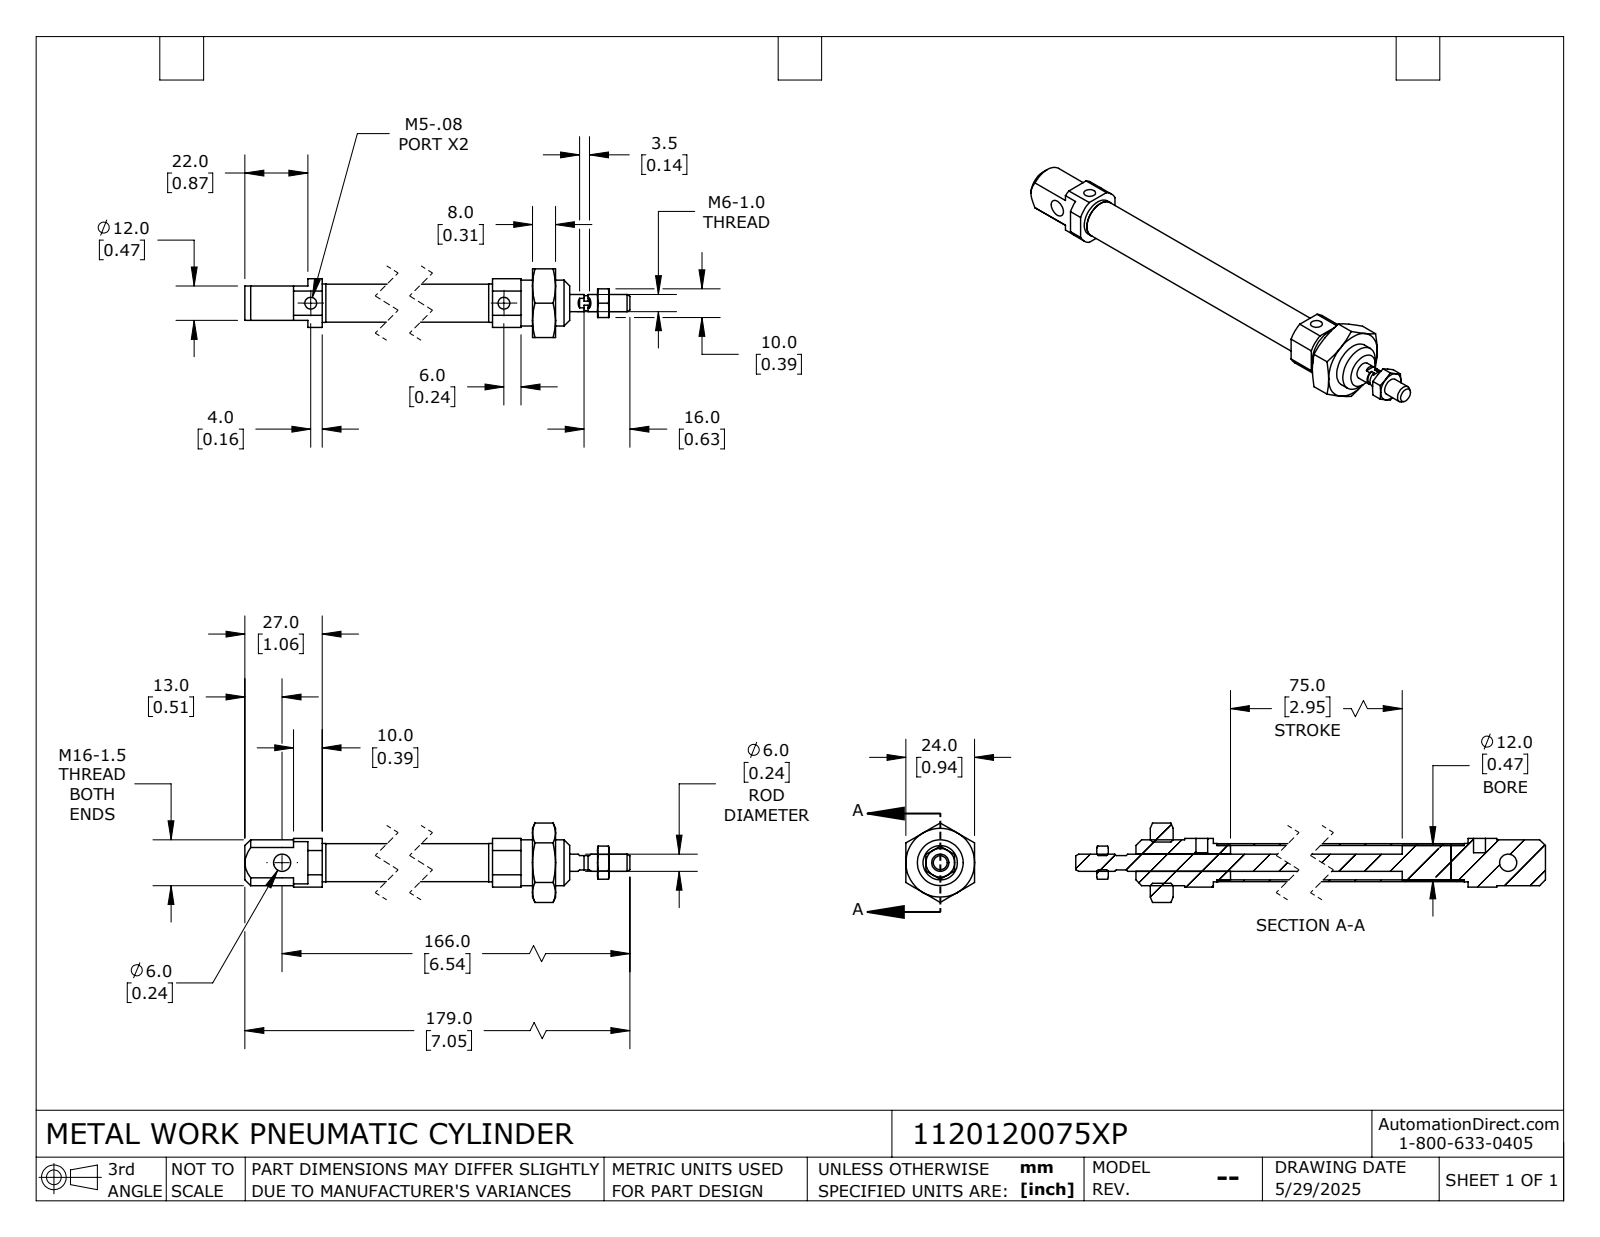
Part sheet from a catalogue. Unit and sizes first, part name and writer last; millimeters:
Units: millimetres
Overall size (bounding box): 179 × 27.71 × 24
Round holes (diameter × count): ⌀4.13 ×2, ⌀4.92 ×1, ⌀6 ×1, ⌀14.38 ×1
Round bosses / shafts (diameter × count): ⌀16 ×1, ⌀13.4 ×1, ⌀13.27 ×1, ⌀12 ×1, ⌀6 ×1, ⌀5.2 ×1
Partial cylindrical surfaces — rounded edges, fillets, slot ends (radius × count): R9.5 ×1
Main face-to-face distances: 17, 6, 24, 12, 131, 2.5, 14.5, 8, 3.5, 33
Hole centre spacings: 112
Volume: 22 137 mm³ · Surface area: 18 429 mm²
Bodies: 6 solids, 139 faces (56 planar, 45 cylindrical, 38 other)
Part name (STEP PRODUCT): 1120120075XP_ROD; 1120120075XP; 1120120075XP_BODY
STEP written by: SolidWorks 2024 (CONFIG_CONTROL_DESIGN)
